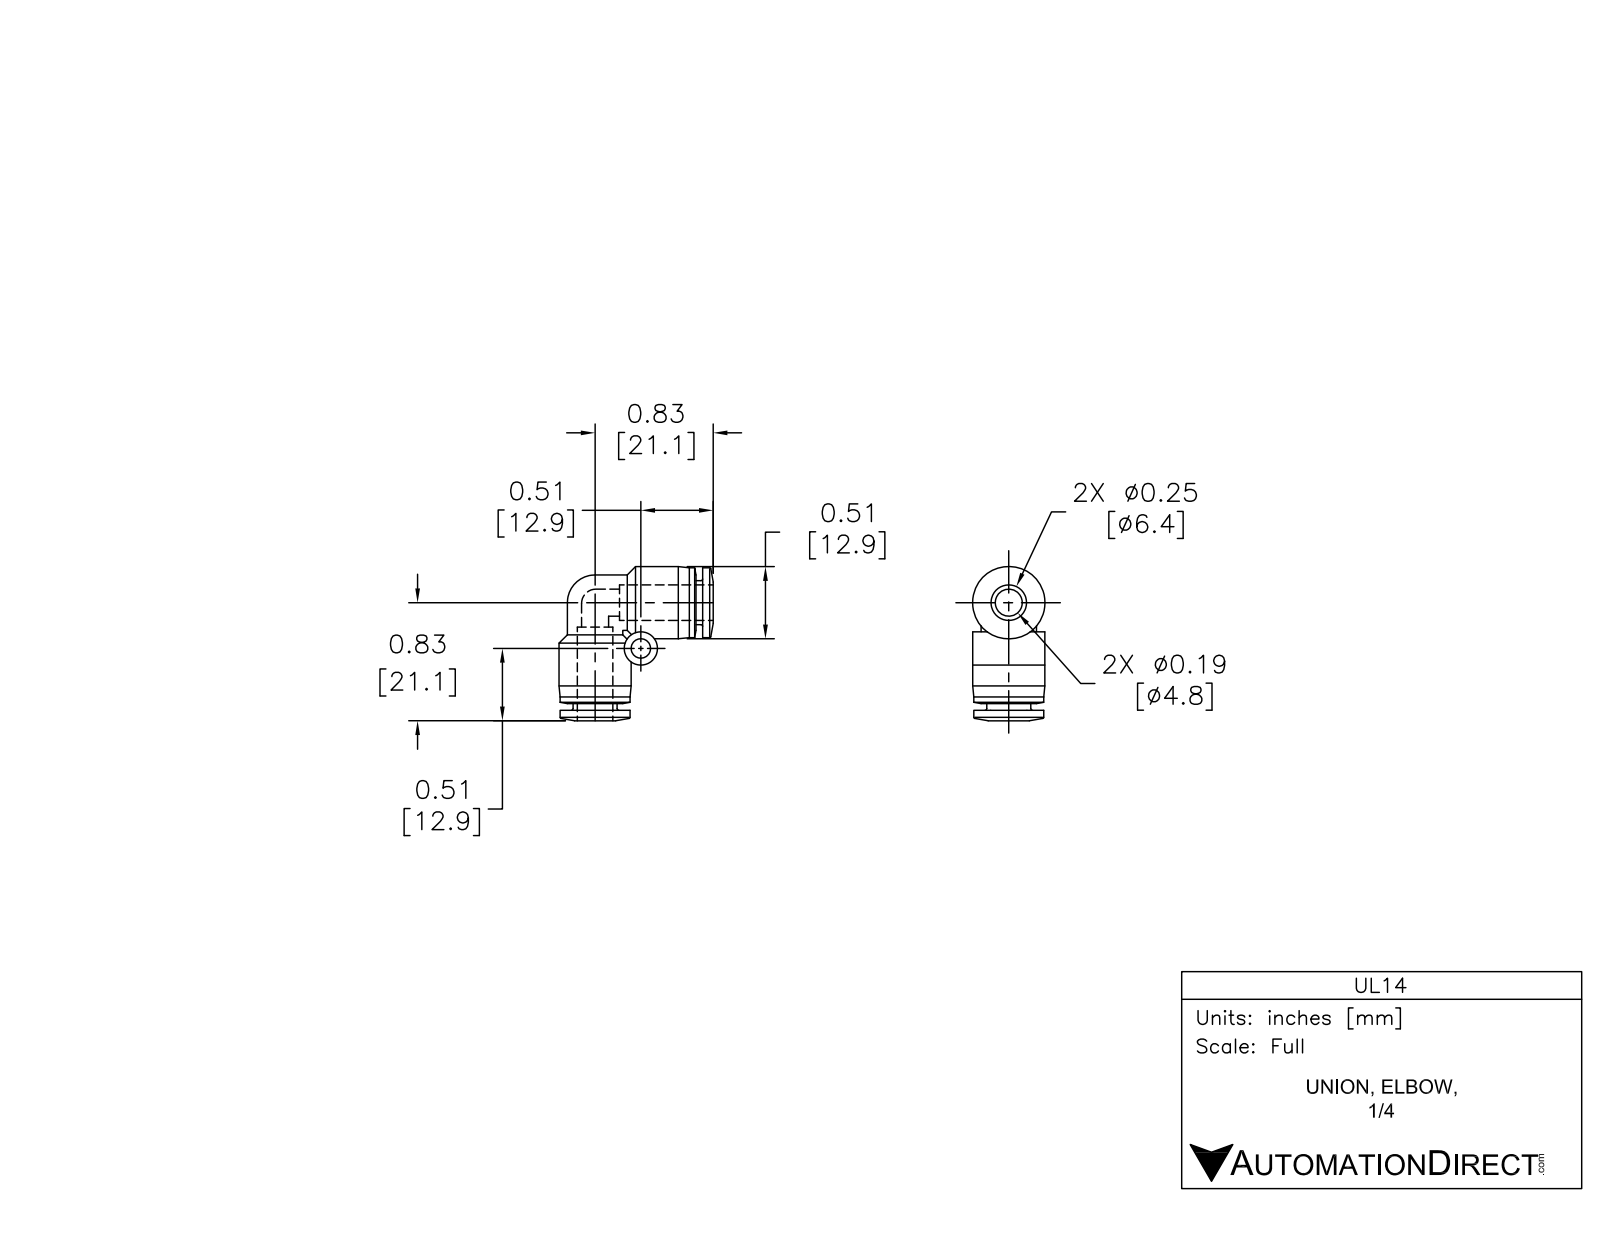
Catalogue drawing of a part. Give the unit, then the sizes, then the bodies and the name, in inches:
Units: inches
Overall size (bounding box): 1.094 × 1.094 × 0.512
Round holes (diameter × count): ⌀0.189 ×2, ⌀0.258 ×2, ⌀0.138 ×1
Round bosses / shafts (diameter × count): ⌀0.512 ×2, ⌀0.496 ×2, ⌀0.394 ×2, ⌀0.313 ×2, ⌀0.236 ×1
Main face-to-face distances: 0.047, 0.539, 0.587, 0.512
Volume: 0.214 in³ · Surface area: 4.911 in²
Bodies: 1 solid, 76 faces (8 planar, 32 cylindrical, 36 other)
Part name (STEP PRODUCT): UL14
STEP written by: SolidWorks 2015 (AUTOMOTIVE_DESIGN)
